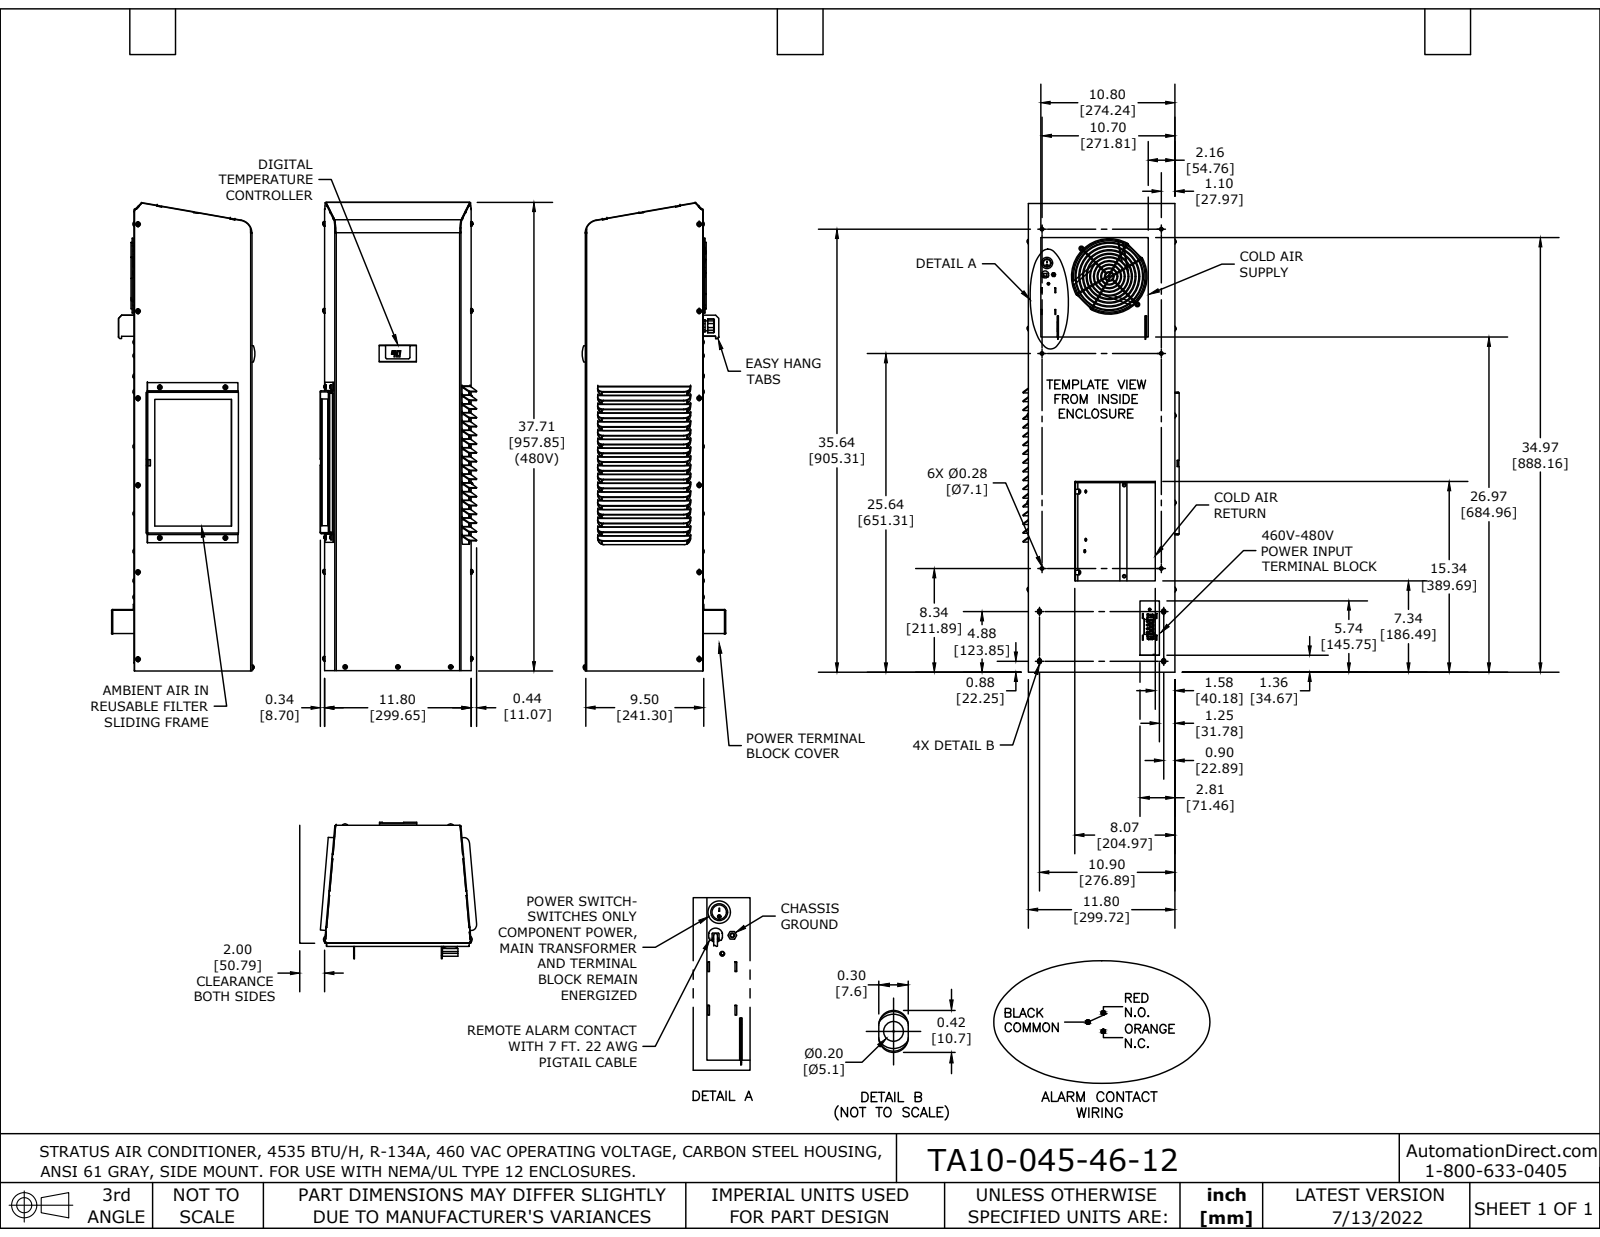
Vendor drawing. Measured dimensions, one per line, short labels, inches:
name: TA10-045-46-12
written by: SolidWorks 2021 (AUTOMOTIVE_DESIGN)
unit: in
bodies: 1 solid, 1744 faces (1077 planar, 497 cylindrical, 170 other)
size: 32.024 × 12.576 × 11.549
volume: 136.5 in³; area: 3 197 in²
holes: 11× ⌀0.159, 5× ⌀0.204, 1× ⌀6
bosses: 7× ⌀0.19, 2× ⌀0.379, 2× ⌀0.353, 2× ⌀0.248, 1× ⌀6.07, 1× ⌀0.906, 1× ⌀0.087
rounds: 45× R0.015, 42× R0.01, 36× R0.5, 36× R0.506, 28× R0.1, 21× R0.058, 21× R0.116, 13× R0.03
face distances: 0.058, 9.435, 9.377, 0.058, 9.493, 0.09, 0.25, 0.308, 9.685, 9.743
hole spacings: 7, 14, 21, 1.732, 5.3, 6.565, 10.869, 12.12
